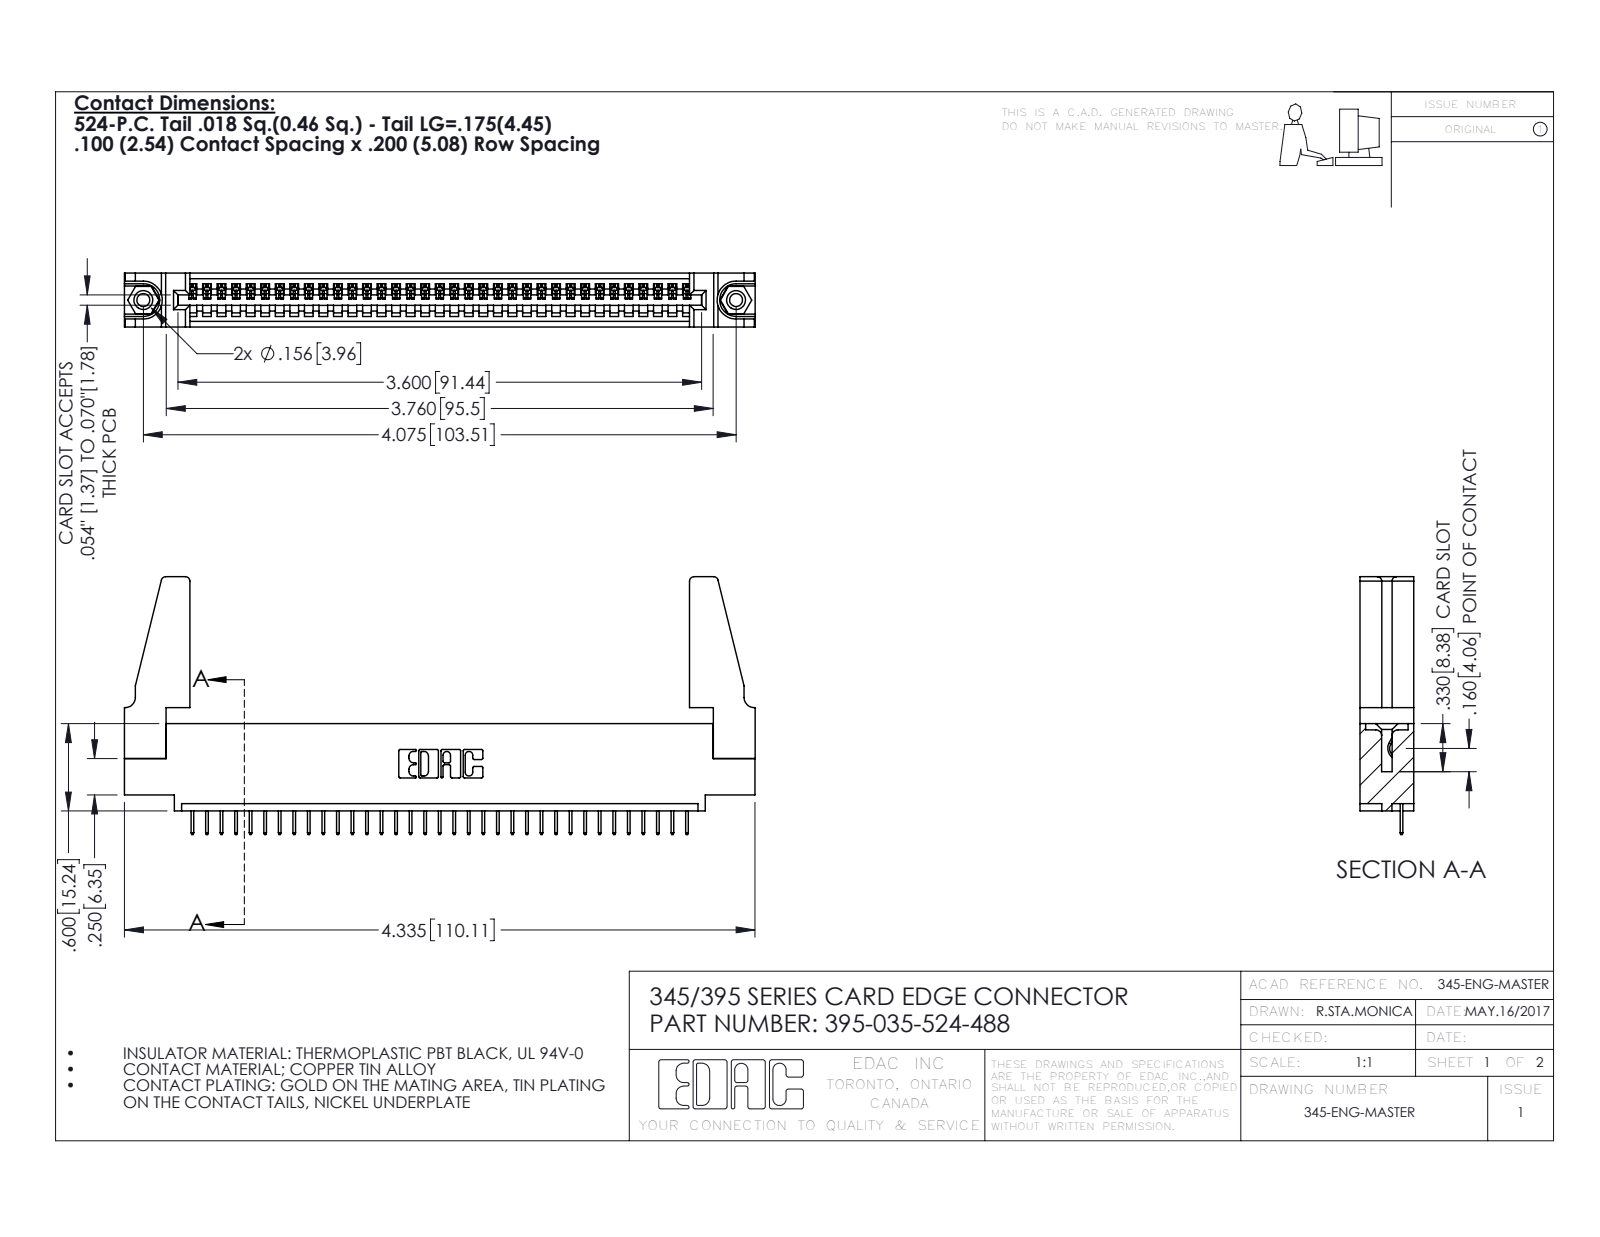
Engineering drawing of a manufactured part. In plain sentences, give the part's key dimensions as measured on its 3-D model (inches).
The part is named "395-035-524-488; 345 Part_0.110 Offset - 0.156 Dia-TH; 345-220-078_345-220-088; 345-292-001_345-293-124 (+1 more)". Its 3-D file was written by "SolidWorks 2016 (CONFIG_CONTROL_DESIGN)". It is 40 solids with 2424 faces: 1766 planar, 642 cylindrical and 16 other. Overall it measures 4.336 by 1.772 by 0.37 inches. Its volume is 0.82 cubic inches and its surface area 25.14 square inches. Round holes: 2 of diameter 0.089, 2 of diameter 0.125, 2 of diameter 0.156, 1 of diameter 0.064. Round bosses or shafts: 2 of diameter 0.155. Partial cylindrical surfaces (rounded edges, fillets, slot ends): 70 of radius 0.006, 22 of radius 0.01, 8 of radius 0.03, 6 of radius 0.007, 6 of radius 0.031, 3 of radius 0.026, 2 of radius 0.031, 2 of radius 0.04. The main face-to-face distances are 0.072, 0.37, 0.298, 0.2, 0.098, 0.272, 0.025, 0.225, 0.072, 0.149. The hole center spacings are 0.27, 3.839, 4.075.
